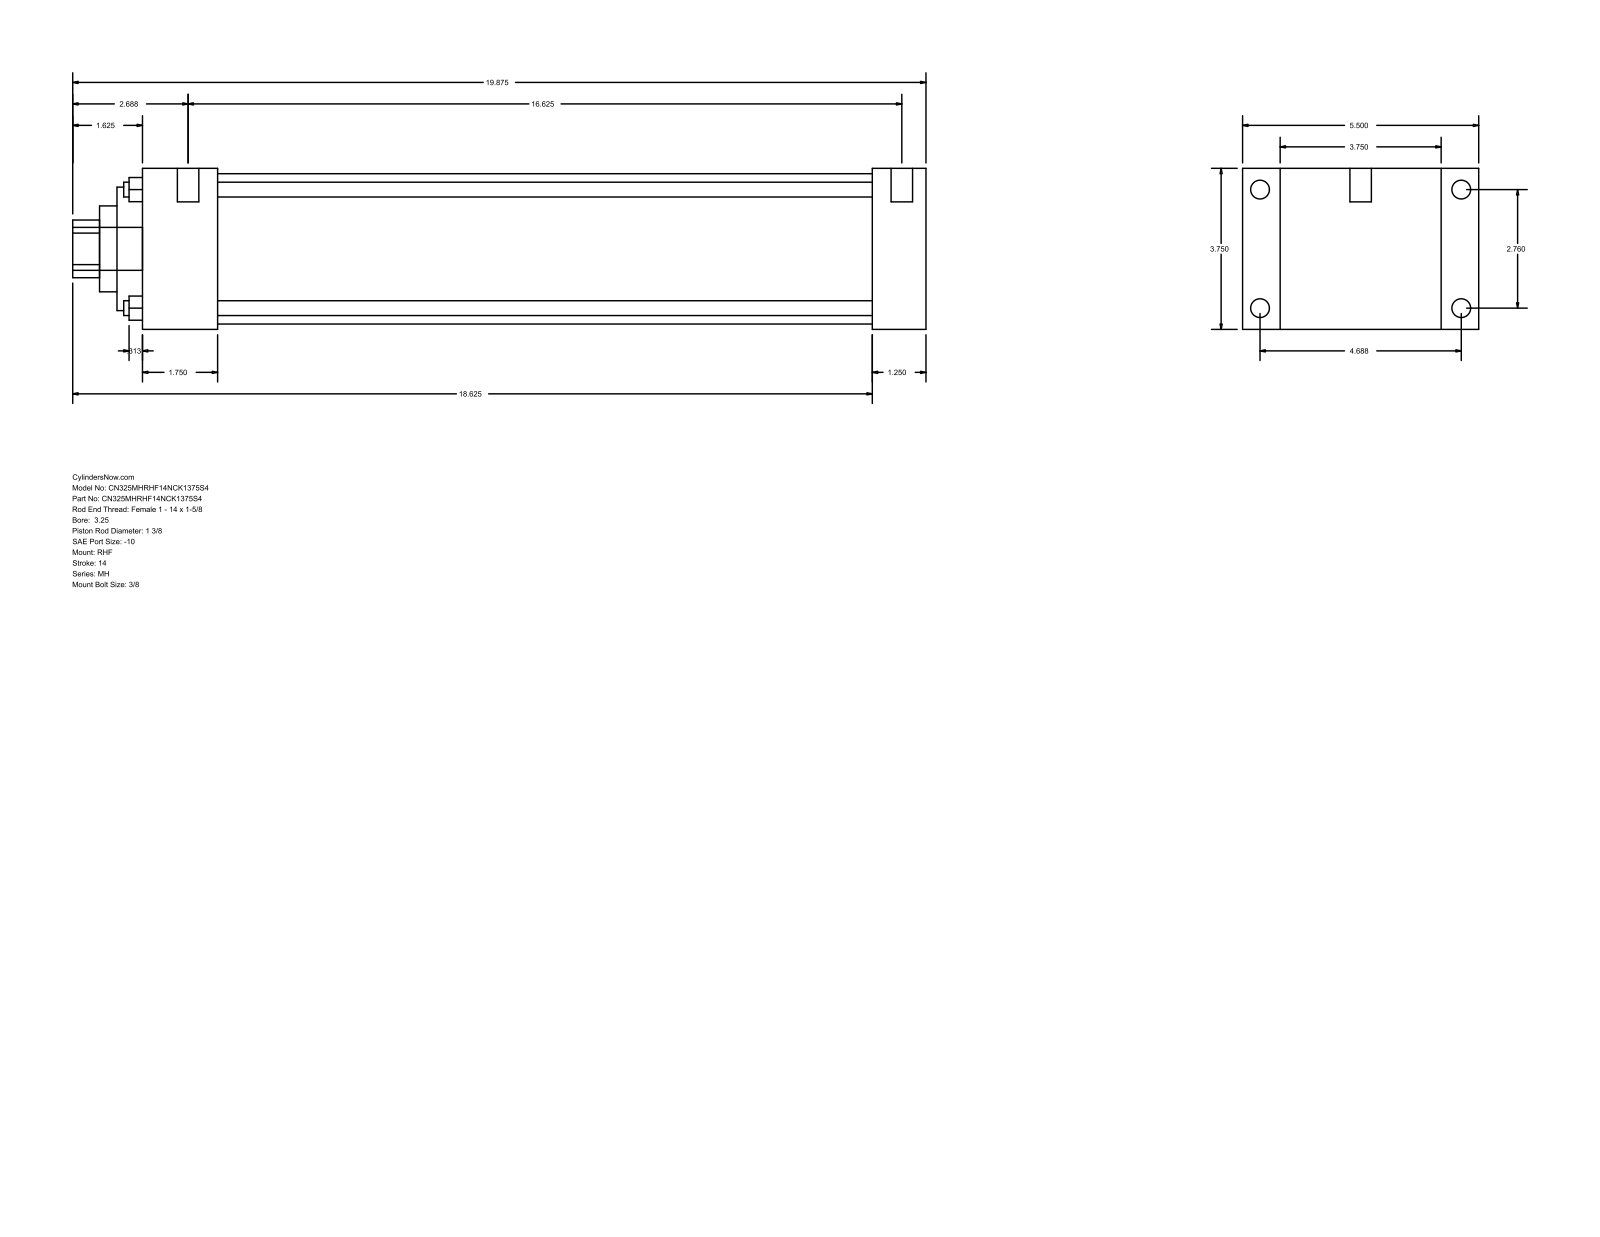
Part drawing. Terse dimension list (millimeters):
name: MH_RHF__0325_1.375
written by: GSSL Pune (CONFIG_CONTROL_DESIGN)
unit: mm
bodies: 0 solids, 90 faces (61 planar, 29 cylindrical, 0 other)
size: 504.82 × 139.7 × 95.25
holes: 4× ⌀8.76, 1× ⌀34.92, 1× ⌀50.8, 1× ⌀73.03, 1× ⌀88.9
bosses: 4× ⌀11.13, 4× ⌀5.56, 2× ⌀12.7, 1× ⌀25.4
rounds: 1× R17.06
face distances: 95.24, 31.75, 22.23, 117.47, 431.8, 463.55, 139.7, 44.45, 387.35, 419.1
hole spacings: 49.57, 70.1, 99.14
